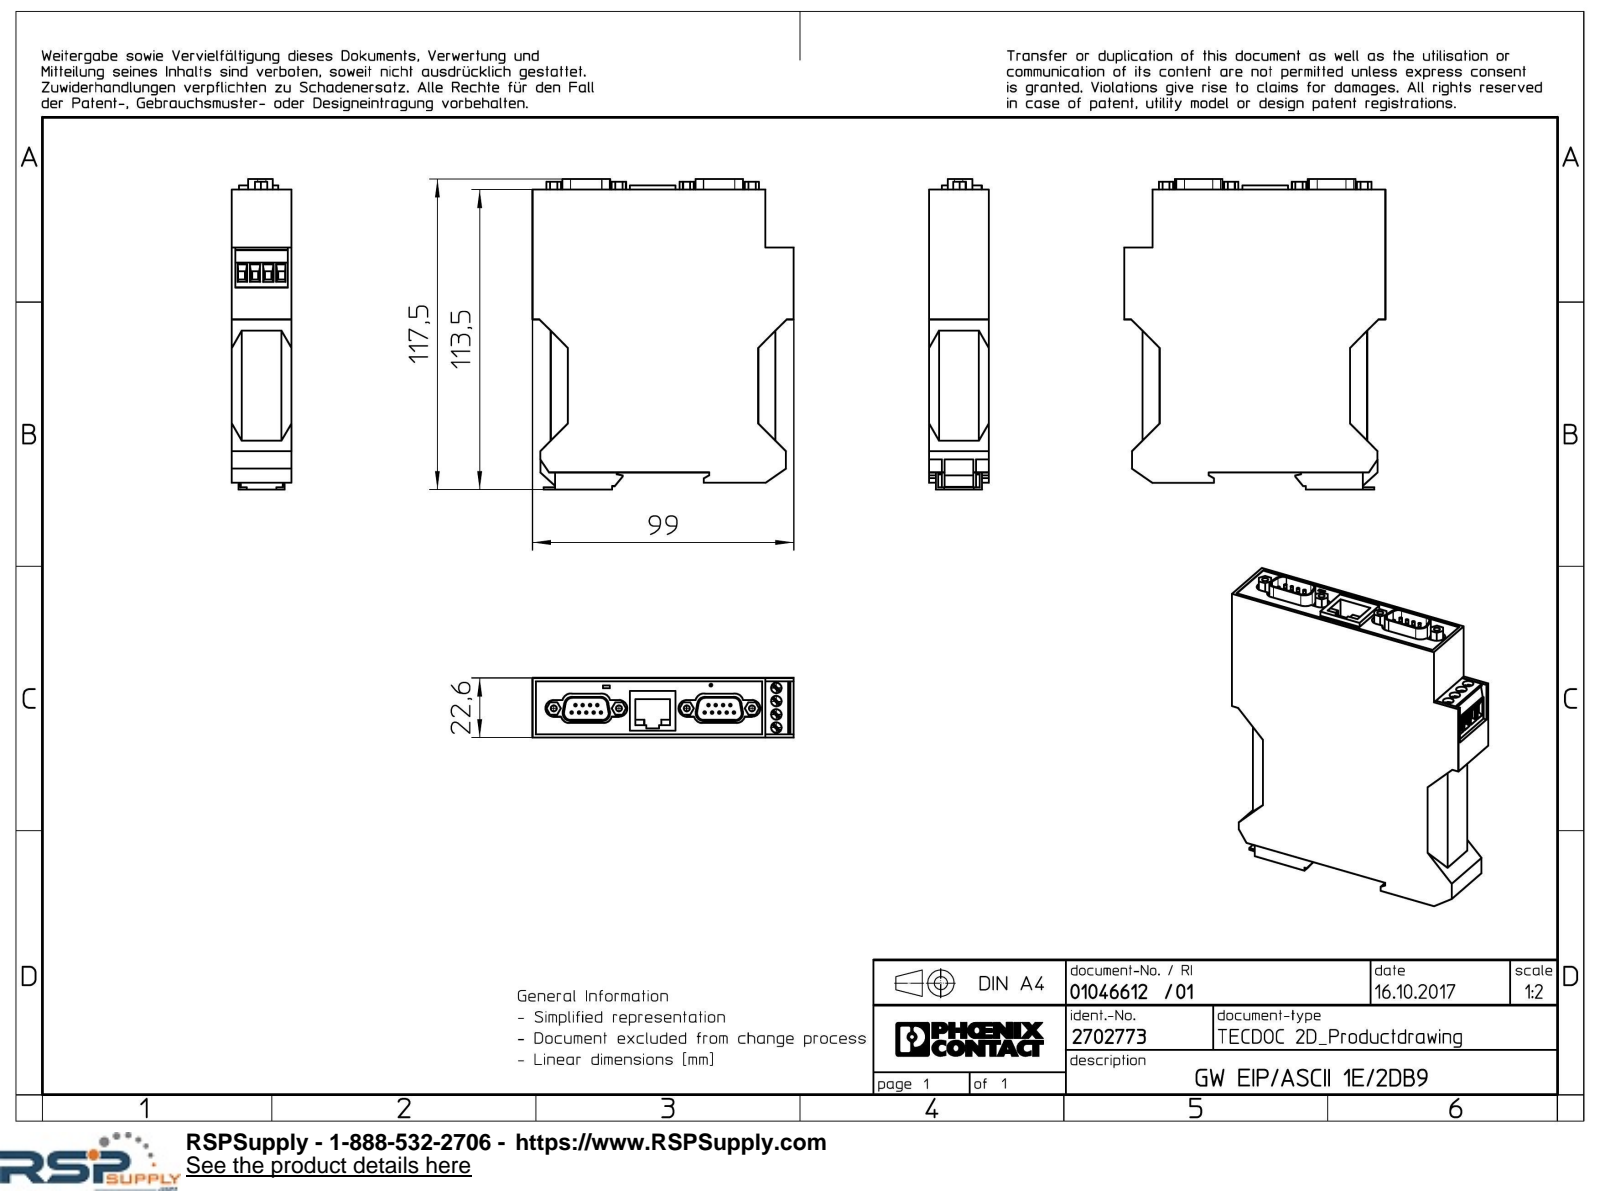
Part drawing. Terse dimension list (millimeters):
name: GW...ASCII_1E_2DB9-select
written by: Creo Elements/Direct Modeling 20.1A 29-Sep-2018 (C) Parametric Technology GmbH (AUTOMOTIVE_DESIGN)
unit: mm
bodies: 1 solid, 362 faces (280 planar, 82 cylindrical, 0 other)
size: 117.5 × 99 × 22.6
volume: 218 275 mm³; area: 32 827 mm²
holes: 4× ⌀2.29, 4× ⌀4, 1× ⌀1.08
bosses: 18× ⌀1
rounds: 12× R3.17, 8× R2.54, 8× R3.04
face distances: 22.6, 4, 92.05, 6.95, 106.8, 110.8, 85.1, 88.3, 81.35, 3.75
hole spacings: 5, 10, 24.74, 50.4, 9.48, 9.6, 11.73, 12.02
